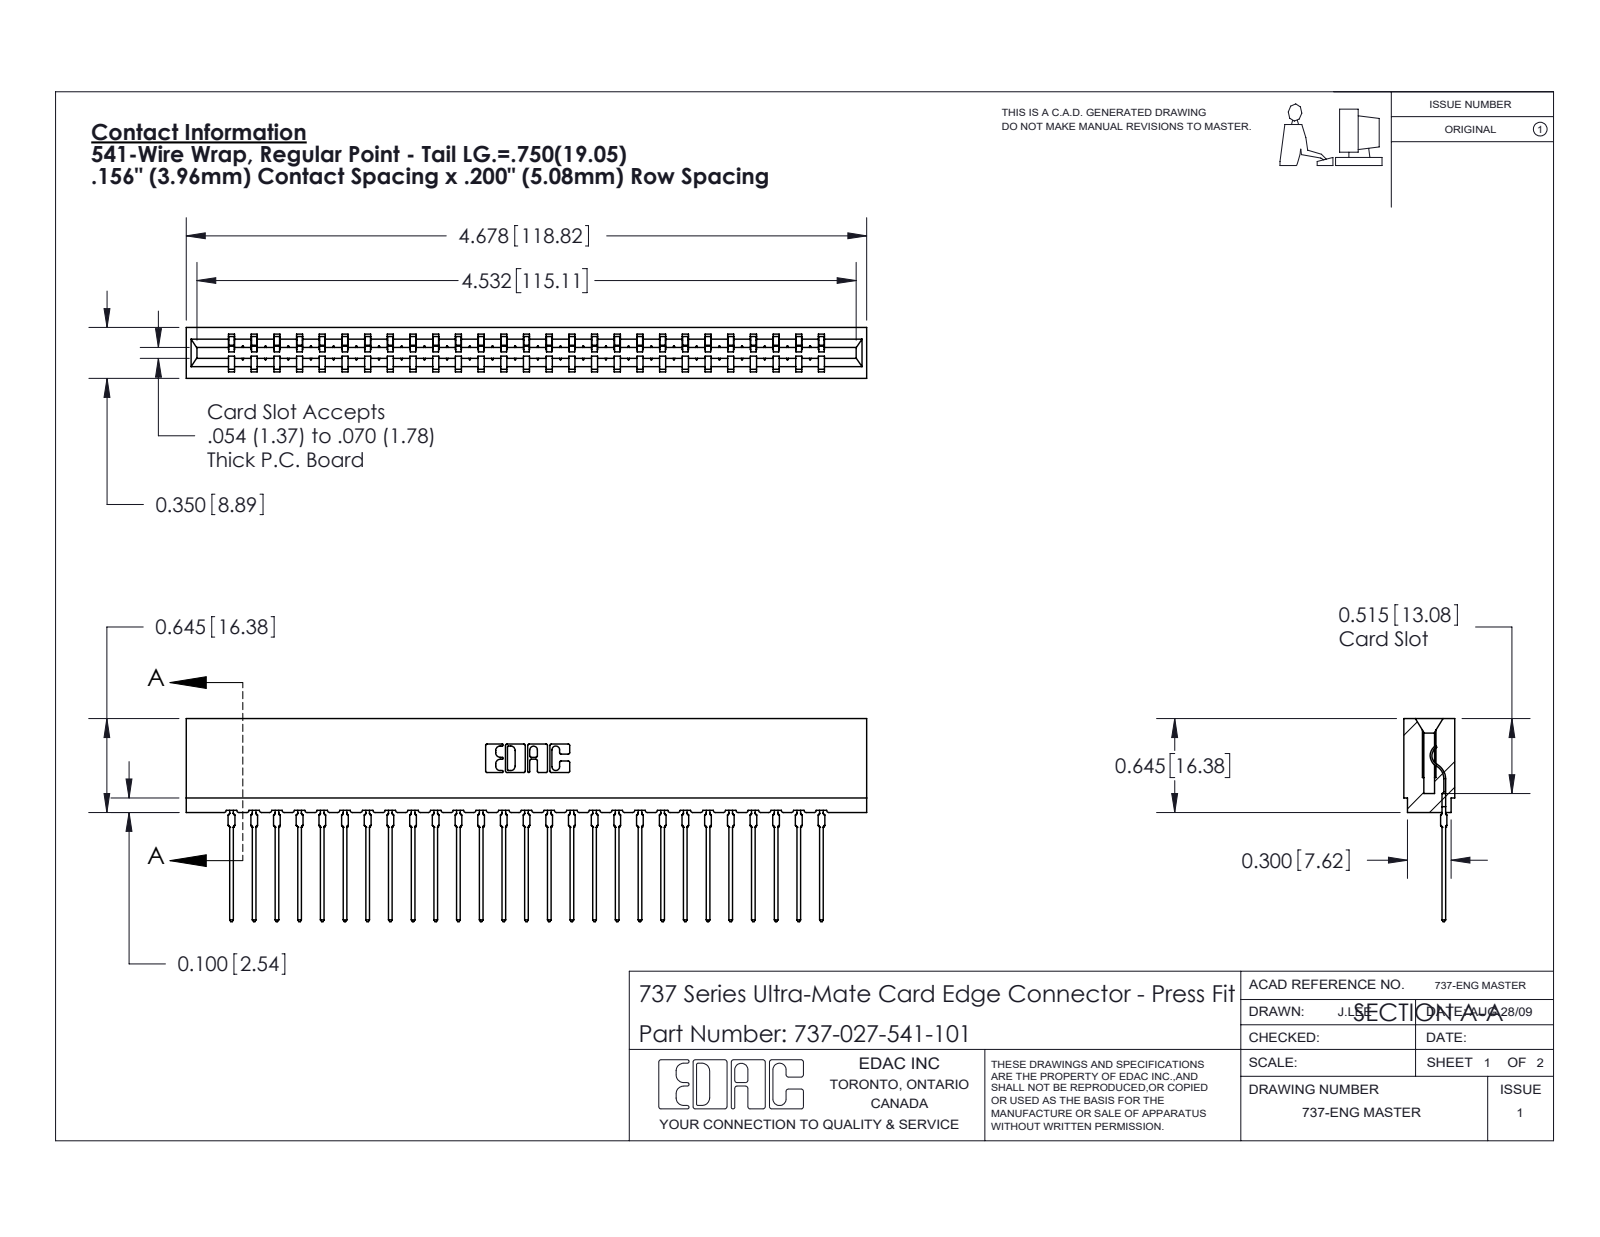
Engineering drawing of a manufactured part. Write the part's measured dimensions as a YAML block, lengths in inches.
part_name: "737 Part_Insulator Option - 01; 745-292-001_541; 737-027-541-101"
step_written_by: "SolidWorks 2020 (CONFIG_CONTROL_DESIGN)"
units: inches
bodies: {solids: 28, faces: 3145, planar: 1890, cylindrical: 553, other: 702}
overall_size: [4.678, 1.396, 0.35]
volume: 0.714
surface_area: 24.86
partial_cylinders:
  - {radius: 0.015, count: 54}
  - {radius: 0.021, count: 54}
  - {radius: 0.01, count: 22}
  - {radius: 0.007, count: 6}
  - {radius: 0.031, count: 6}
  - {radius: 0.005, count: 4}
  - {radius: 0.011, count: 4}
  - {radius: 0.026, count: 3}
face_to_face_distances: [0.138, 0.212, 0.35, 0.624, 0.156, 0.074, 0.063, 0.287, 0.076, 0.149]
